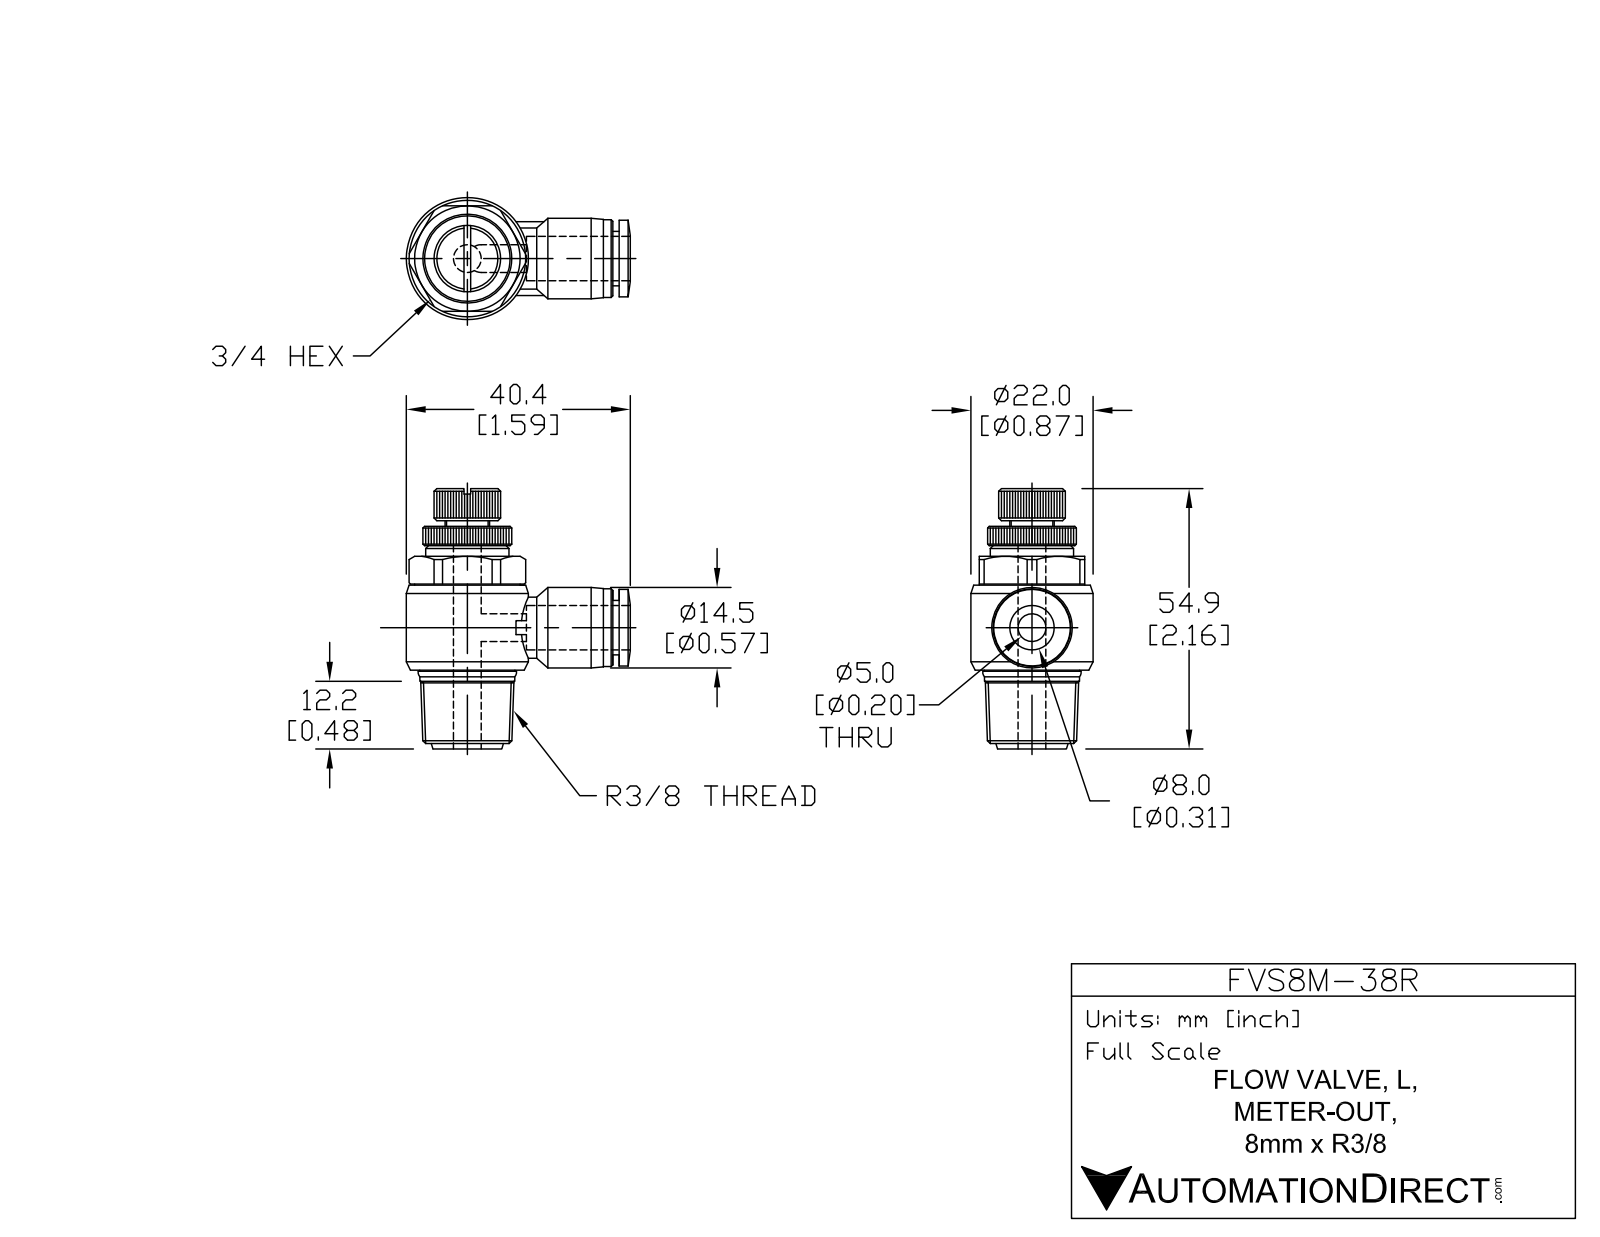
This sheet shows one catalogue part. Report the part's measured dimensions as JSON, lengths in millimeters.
{"part_name": "FVS8M-38R", "step_written_by": "SolidWorks 2015 (AUTOMOTIVE_DESIGN)", "units": "millimeters", "bodies": {"solids": 1, "faces": 565, "planar": 254, "cylindrical": 145, "other": 166}, "overall_size": [54.9, 40.4, 22], "volume_mm3": 13700, "surface_area_mm2": 5752, "round_holes": [[4.3, 2], [8.3, 1]], "round_bosses_or_shafts": [[22, 1], [19, 1], [17.1, 1], [17.1, 1], [15, 1], [14.5, 1], [14, 1], [13.8, 1]], "partial_cylinders_radius": [[6, 1], [8, 1], [10.5, 1]], "face_to_face_distances": [19, 5.8, 34.7, 40.5, 14.2, 20.5, 26.3, 54.9, 40.7, 20.2]}
